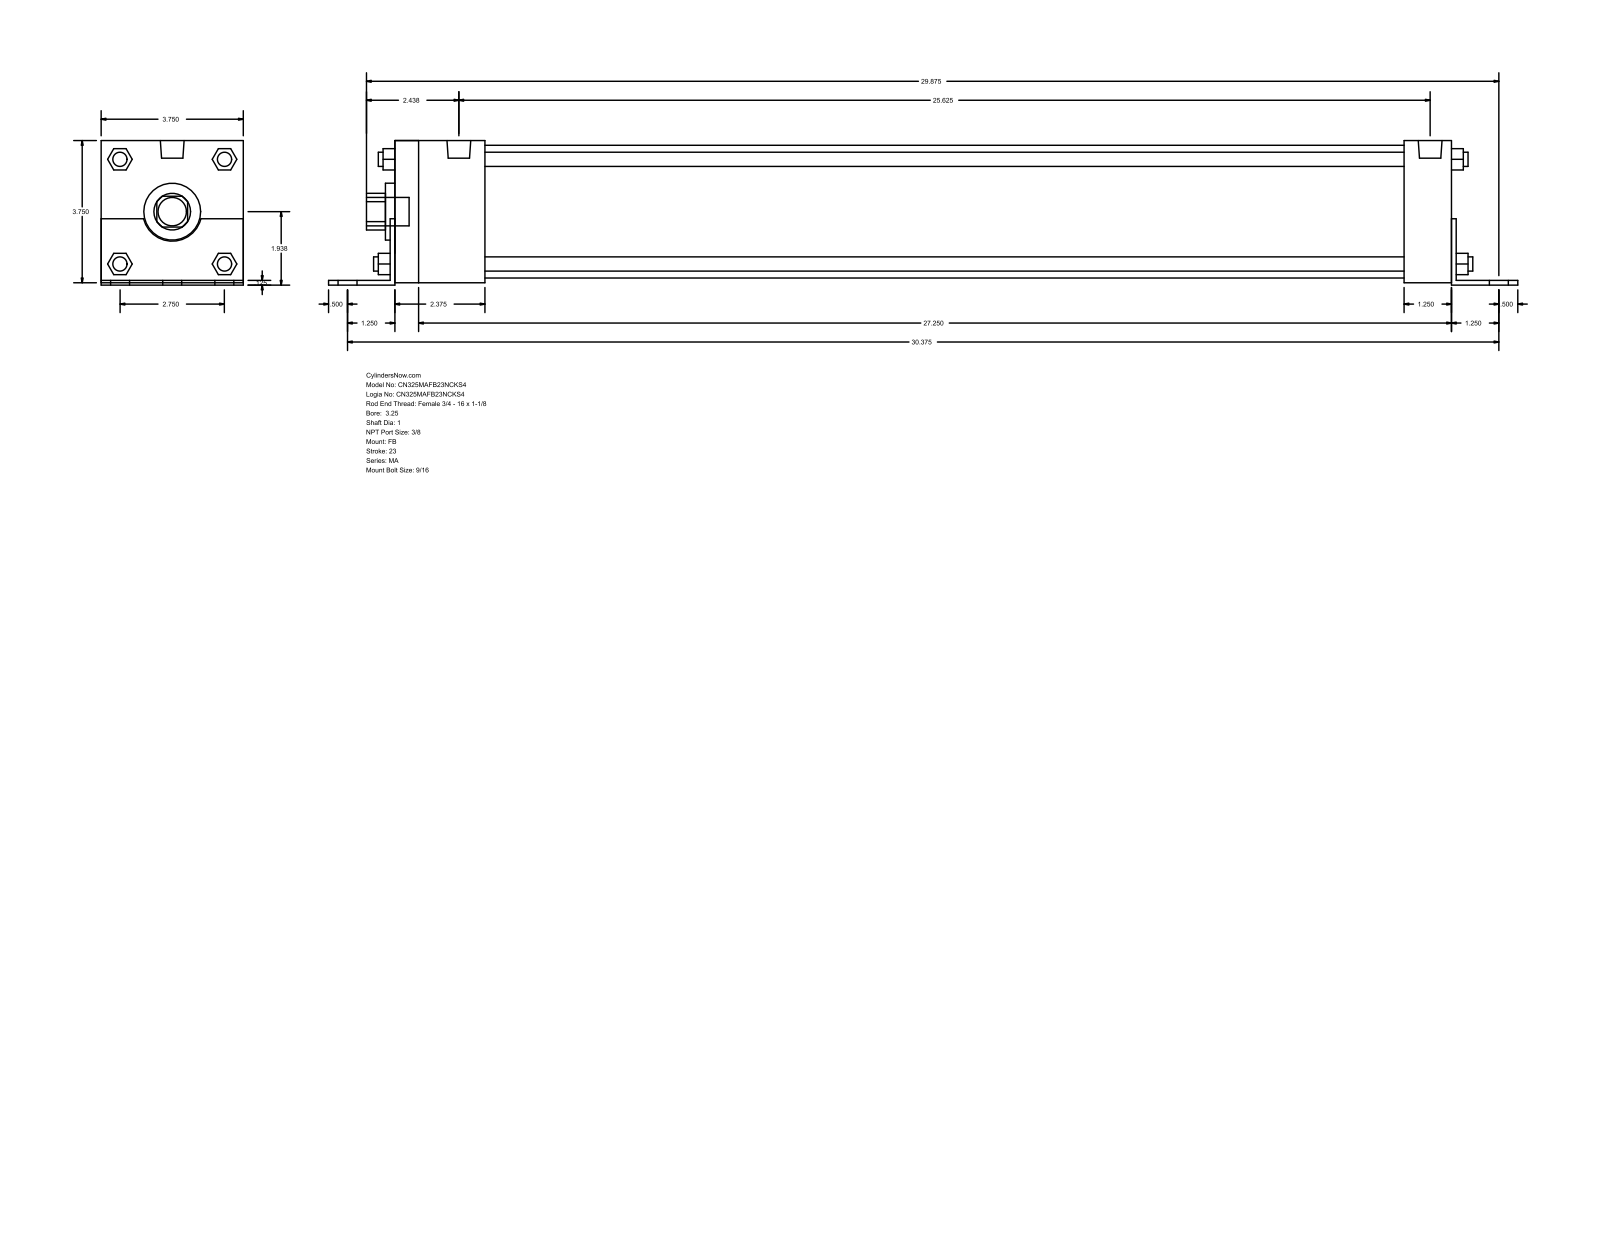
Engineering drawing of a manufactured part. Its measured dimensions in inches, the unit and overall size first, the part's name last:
Units: inches
Overall size (bounding box): 31.375 × 3.813 × 3.75
Round holes (diameter × count): ⌀1 ×1, ⌀1.5 ×1, ⌀3.5 ×1
Round bosses / shafts (diameter × count): ⌀0.563 ×6, ⌀0.437 ×4, ⌀0.375 ×4, ⌀0.627 ×2, ⌀0.75 ×1
Partial cylindrical surfaces — rounded edges, fillets, slot ends (radius × count): R0.484 ×1, R0.78 ×1
Main face-to-face distances: 3.75, 0.125, 0.063, 3.812, 0.062, 3.687, 28, 27.875, 28.125, 26.75
Bodies: 0 solids, 140 faces (105 planar, 35 cylindrical, 0 other)
Part name (STEP PRODUCT): MA_FB__0325_1
STEP written by: GSSL Pune (CONFIG_CONTROL_DESIGN)
